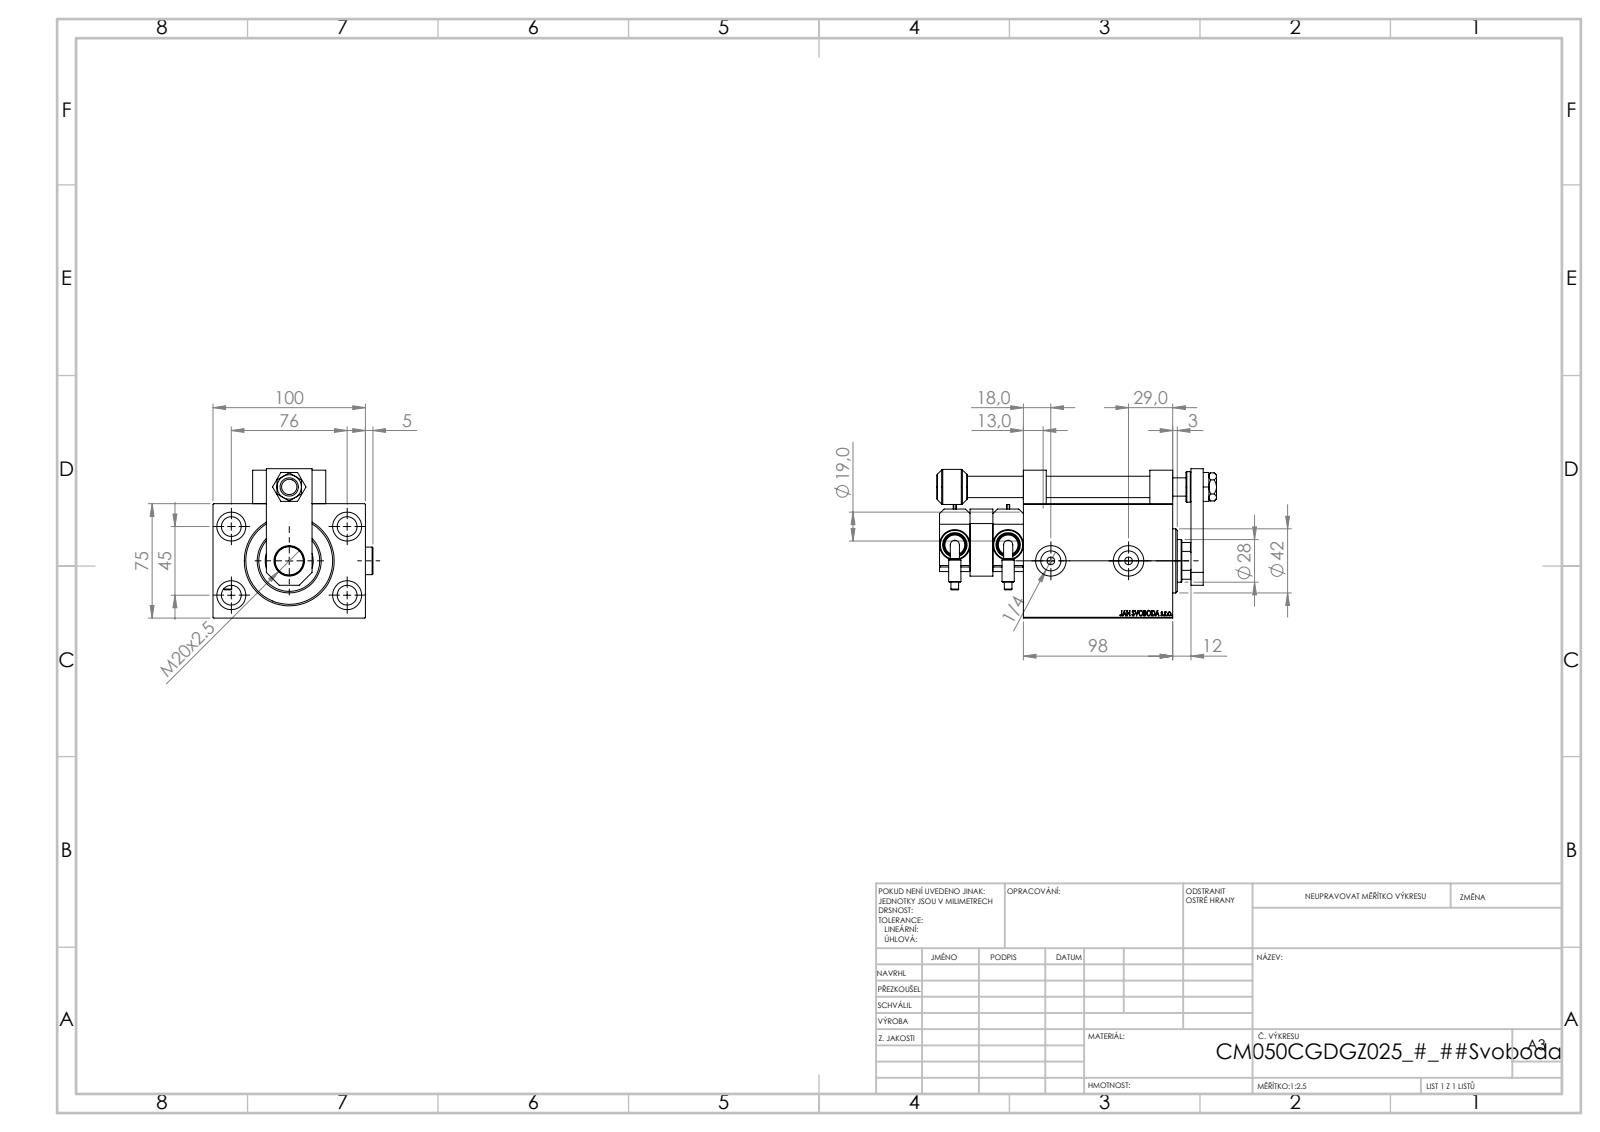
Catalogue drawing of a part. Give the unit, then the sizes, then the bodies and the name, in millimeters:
Units: millimetres
Overall size (bounding box): 183.5 × 104.9 × 98
Round holes (diameter × count): ⌀13 ×5, ⌀4 ×4, ⌀8 ×4, ⌀19 ×4, ⌀20 ×3, ⌀5 ×2, ⌀13.16 ×2, ⌀12 ×1, ⌀14 ×1, ⌀18.5 ×1, ⌀28 ×1, ⌀31.5 ×1
Round bosses / shafts (diameter × count): ⌀20 ×3, ⌀18 ×2, ⌀16 ×2, ⌀14 ×2, ⌀8 ×2, ⌀6 ×2, ⌀5.04 ×2, ⌀42 ×1
Partial cylindrical surfaces — rounded edges, fillets, slot ends (radius × count): R3 ×1, R13.5 ×1
Main face-to-face distances: 75, 35, 20, 100, 98, 118, 15, 70, 49, 12
Hole centre spacings: 44.16, 20, 45, 46.04, 76, 80.53, 83, 85.38
Volume: 793 430 mm³ · Surface area: 157 835 mm²
Bodies: 16 solids, 1172 faces (559 planar, 144 cylindrical, 469 other)
Part name (STEP PRODUCT): SWITCH_P_FRONT_BACK; ZARAZKA_P; Zatka_OIL_PORT; MIDDLE (+7 more)
STEP written by: SolidWorks 2019 (CONFIG_CONTROL_DESIGN)
